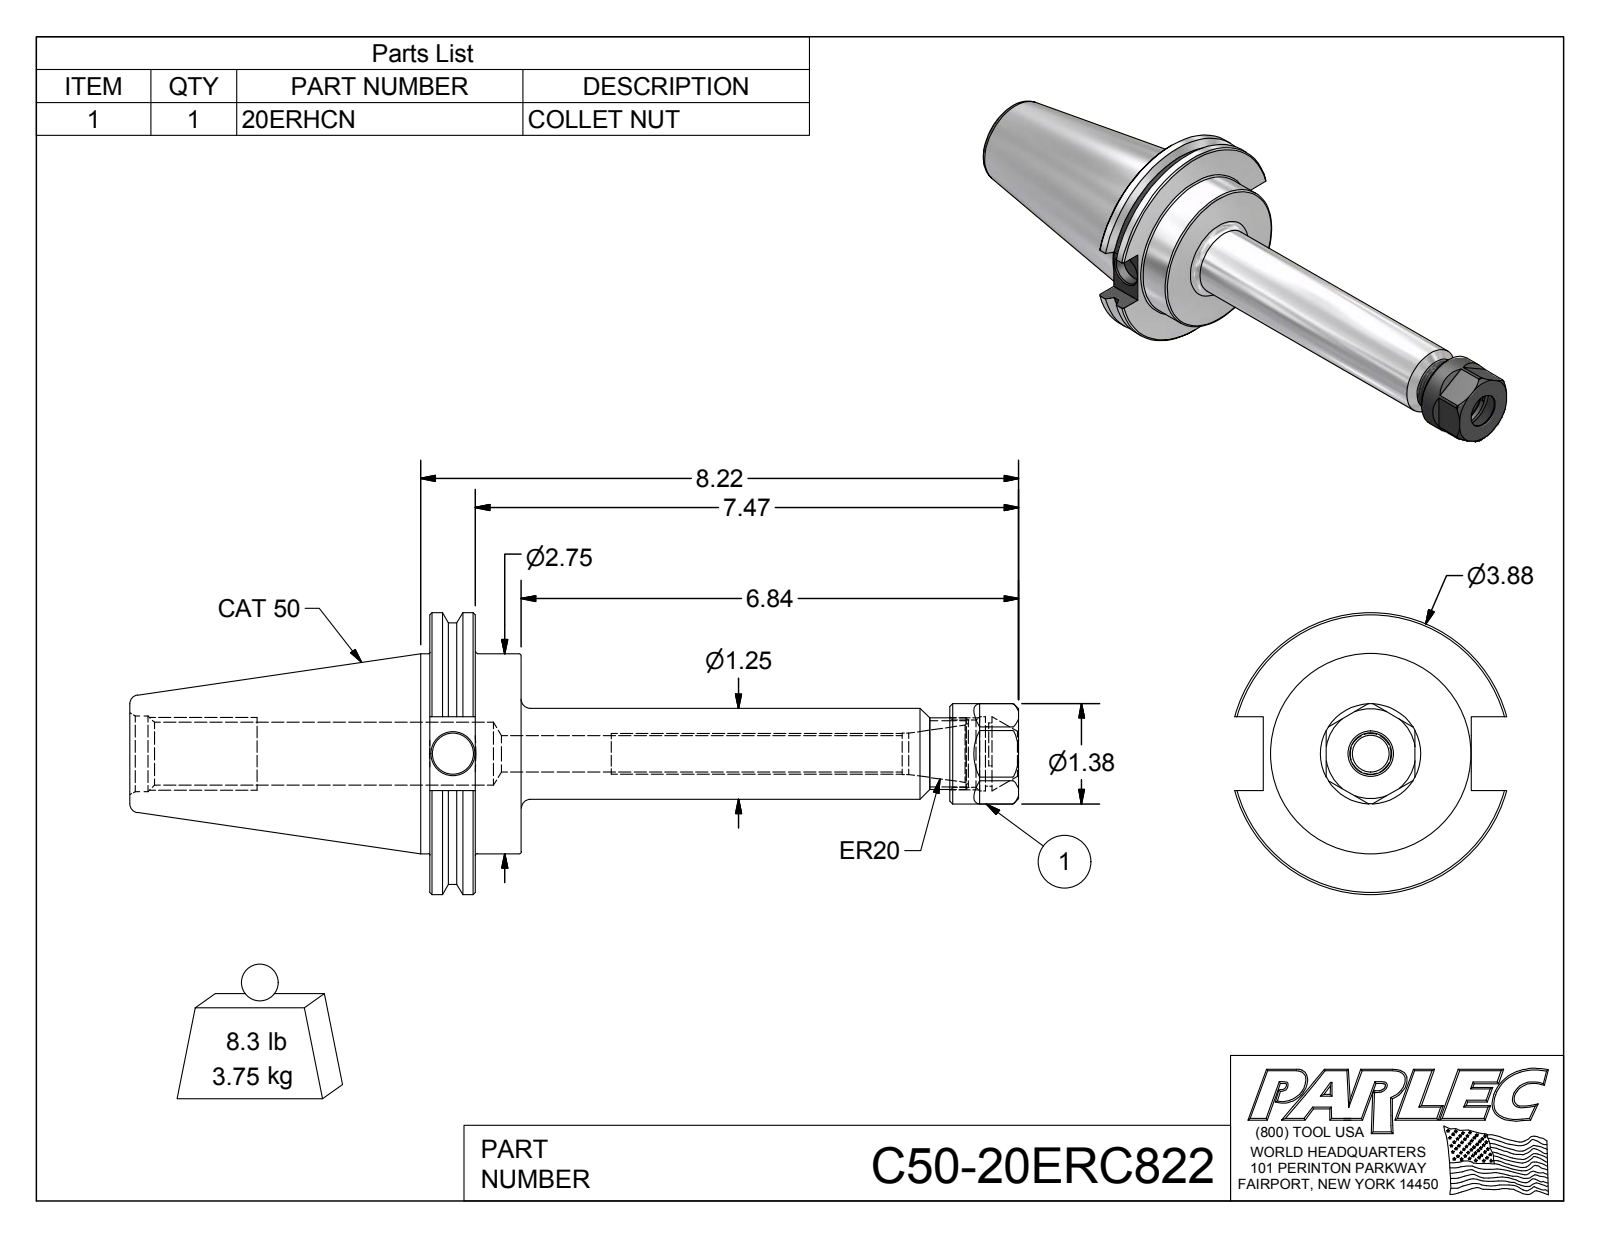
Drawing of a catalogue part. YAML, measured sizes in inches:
part_name: "C50-20ERC822; C50-20ER8-1; 20ERHCN"
step_written_by: "Autodesk Inventor 2012 (AUTOMOTIVE_DESIGN)"
units: inches
bodies: {solids: 2, faces: 89, planar: 29, cylindrical: 21, other: 39}
overall_size: [12.22, 3.875, 3.74]
volume: 29.49
surface_area: 116.9
round_holes:
  - {diameter: 0.502, count: 1}
  - {diameter: 0.563, count: 1}
  - {diameter: 0.57, count: 1}
  - {diameter: 0.62, count: 1}
  - {diameter: 0.82, count: 1}
  - {diameter: 0.865, count: 1}
  - {diameter: 0.925, count: 1}
  - {diameter: 1.024, count: 1}
  - {diameter: 1.038, count: 1}
round_bosses_or_shafts:
  - {diameter: 3.875, count: 1}
  - {diameter: 3.594, count: 1}
  - {diameter: 2.75, count: 1}
  - {diameter: 1.378, count: 1}
  - {diameter: 1.25, count: 1}
  - {diameter: 0.984, count: 1}
partial_cylinders:
  - {radius: 0.423, count: 1}
face_to_face_distances: [0.625, 1.255, 0.63, 1.22, 8.095, 7.47, 6.84, 7.15, 6.525, 5.895]
hole_center_spacings: [0.037]
